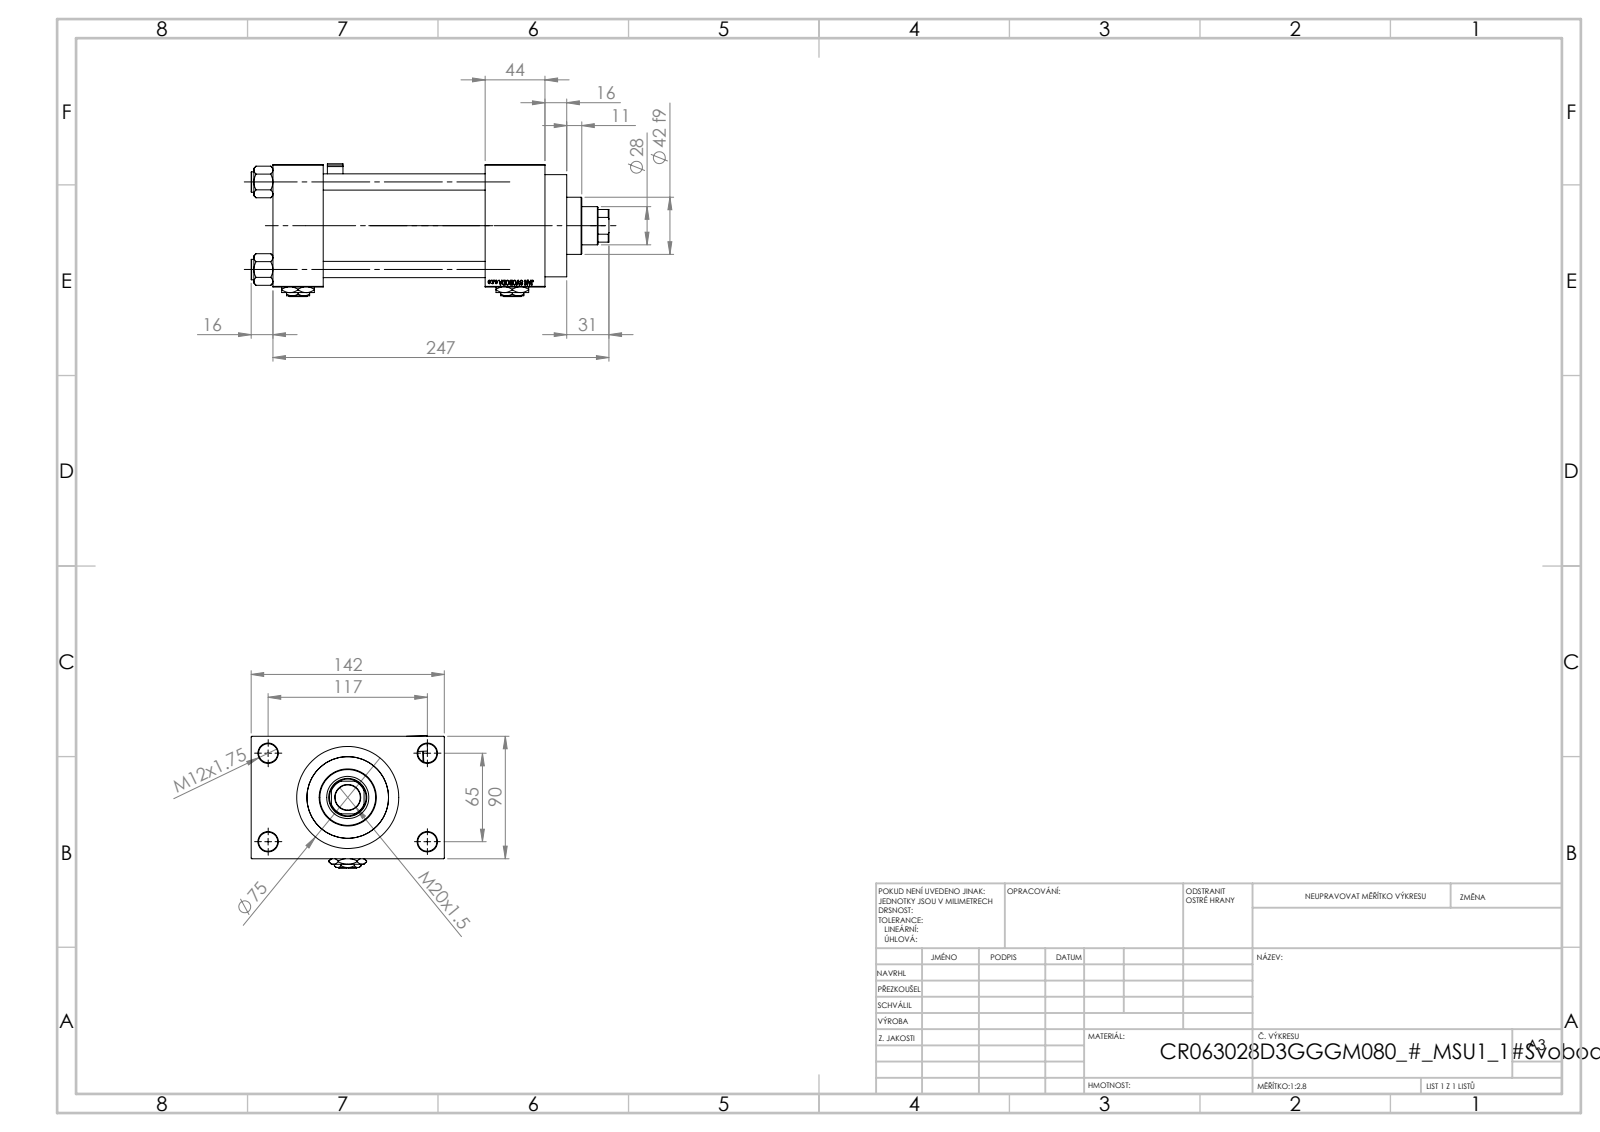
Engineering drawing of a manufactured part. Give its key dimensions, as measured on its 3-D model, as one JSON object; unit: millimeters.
{"part_name": "Zatka_pro_OIL_PORT; V215_VC_A; V215CR_VCP_D; NUT_M5_D (+3 more)", "step_written_by": "SolidWorks 2019 (CONFIG_CONTROL_DESIGN)", "units": "millimeters", "bodies": {"solids": 14, "faces": 1282, "planar": 574, "cylindrical": 130, "other": 578}, "overall_size": [263, 142, 97.53], "volume_mm3": 1222000, "surface_area_mm2": 248578, "round_holes": [[12, 4], [14, 4], [7, 2], [20.96, 2], [30, 2], [18.5, 1], [28, 1], [31, 1], [50, 1], [60, 1], [63, 1]], "round_bosses_or_shafts": [[15, 4], [75, 1], [69, 1], [42, 1], [6, 1]], "partial_cylinders_radius": [[0.5, 24], [1, 1], [2.5, 1], [4, 1], [13.5, 1]], "face_to_face_distances": [90, 119, 37, 156, 163, 200, 44, 116, 26, 142], "hole_center_spacings": [26.35, 45.47, 64.3, 66.92, 69.81, 90.65, 111.34, 65]}
